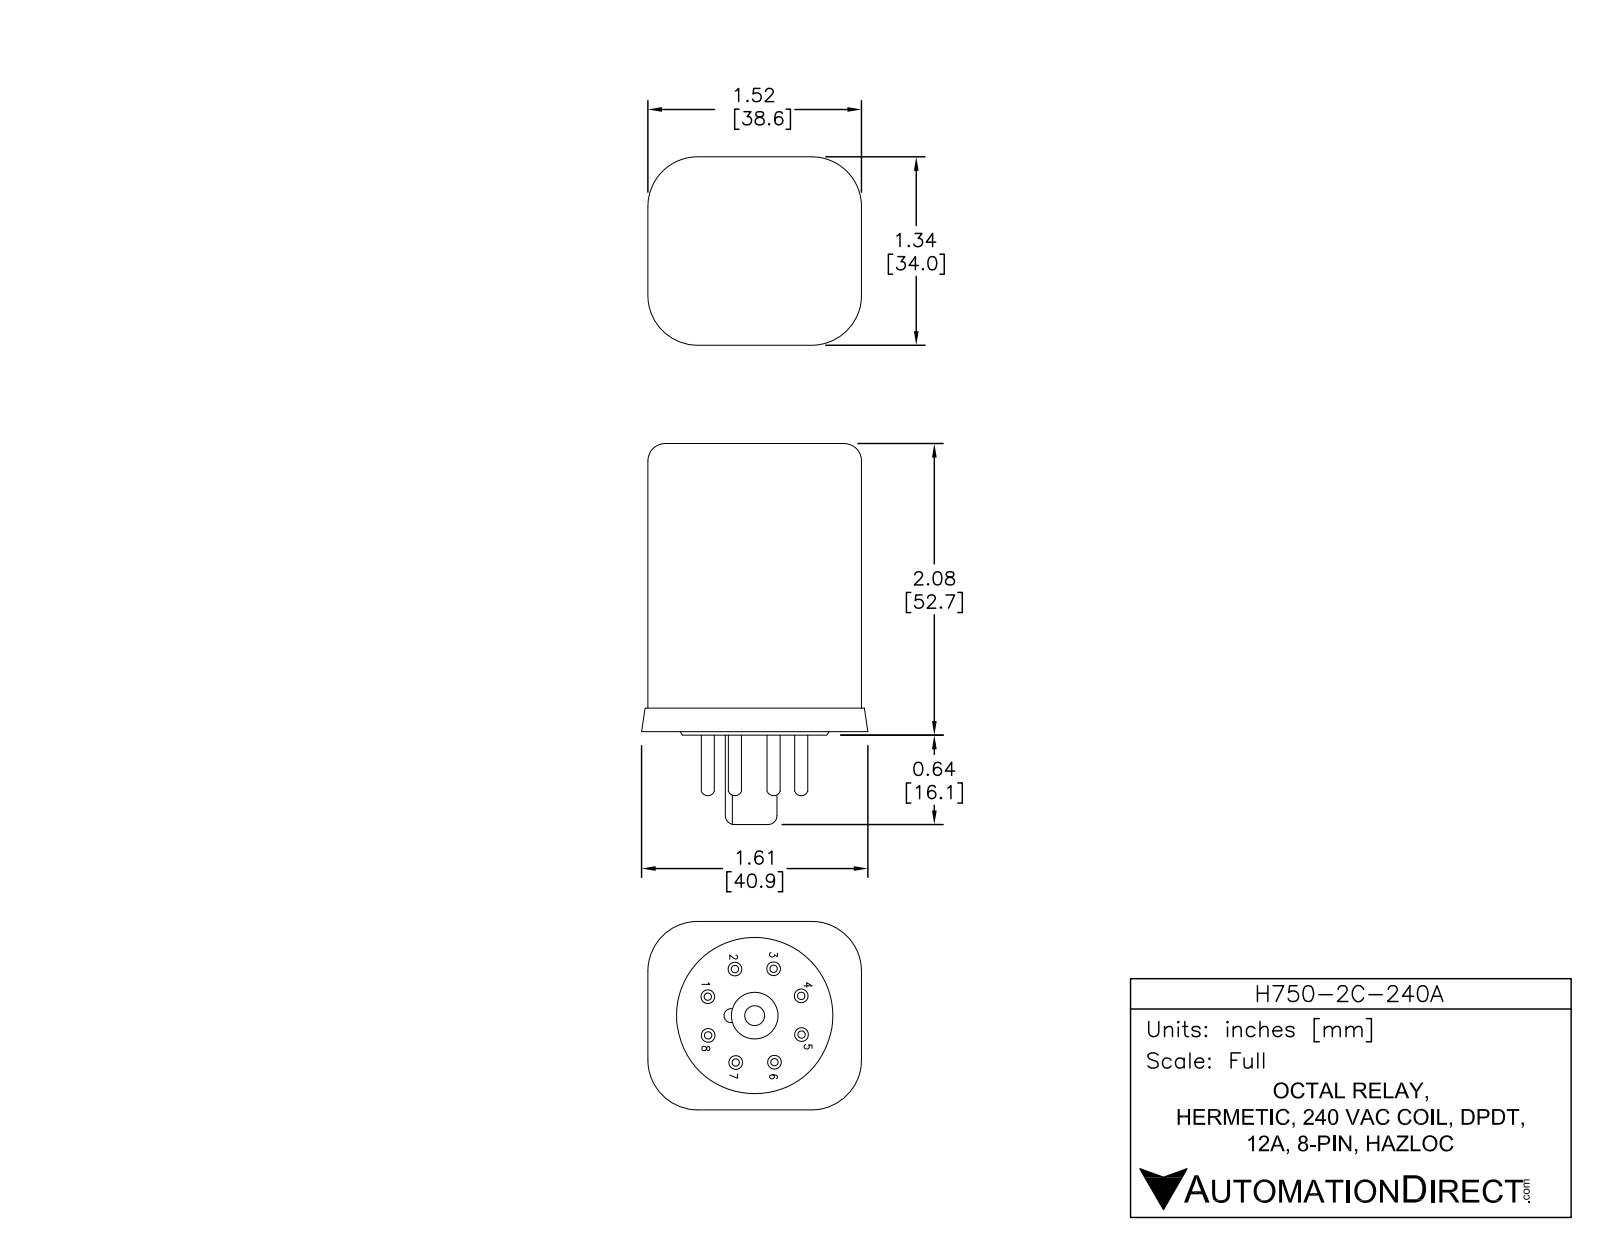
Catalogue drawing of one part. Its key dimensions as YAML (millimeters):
part_name: "H750-2C-240A"
step_written_by: "SolidWorks 2013 (AUTOMOTIVE_DESIGN)"
units: millimeters
bodies: {solids: 1, faces: 286, planar: 125, cylindrical: 65, other: 96}
overall_size: [67.3, 41.35, 36.6]
volume: 66961
surface_area: 10715
round_holes:
  - {diameter: 4.5, count: 8}
  - {diameter: 3.9, count: 1}
round_bosses_or_shafts:
  - {diameter: 2.31, count: 8}
  - {diameter: 27, count: 1}
  - {diameter: 12, count: 1}
  - {diameter: 8, count: 1}
partial_cylinders:
  - {radius: 0.62, count: 8}
  - {radius: 2.5, count: 4}
  - {radius: 10, count: 4}
  - {radius: 11.3, count: 4}
  - {radius: 0.5, count: 2}
  - {radius: 0.59, count: 1}
face_to_face_distances: [53, 34, 38.75, 0.5, 53.5, 1.3, 35.3, 40.05, 1, 54]
hole_center_spacings: [8.5, 12.02, 15.7, 6.5, 6.51, 16.99]
